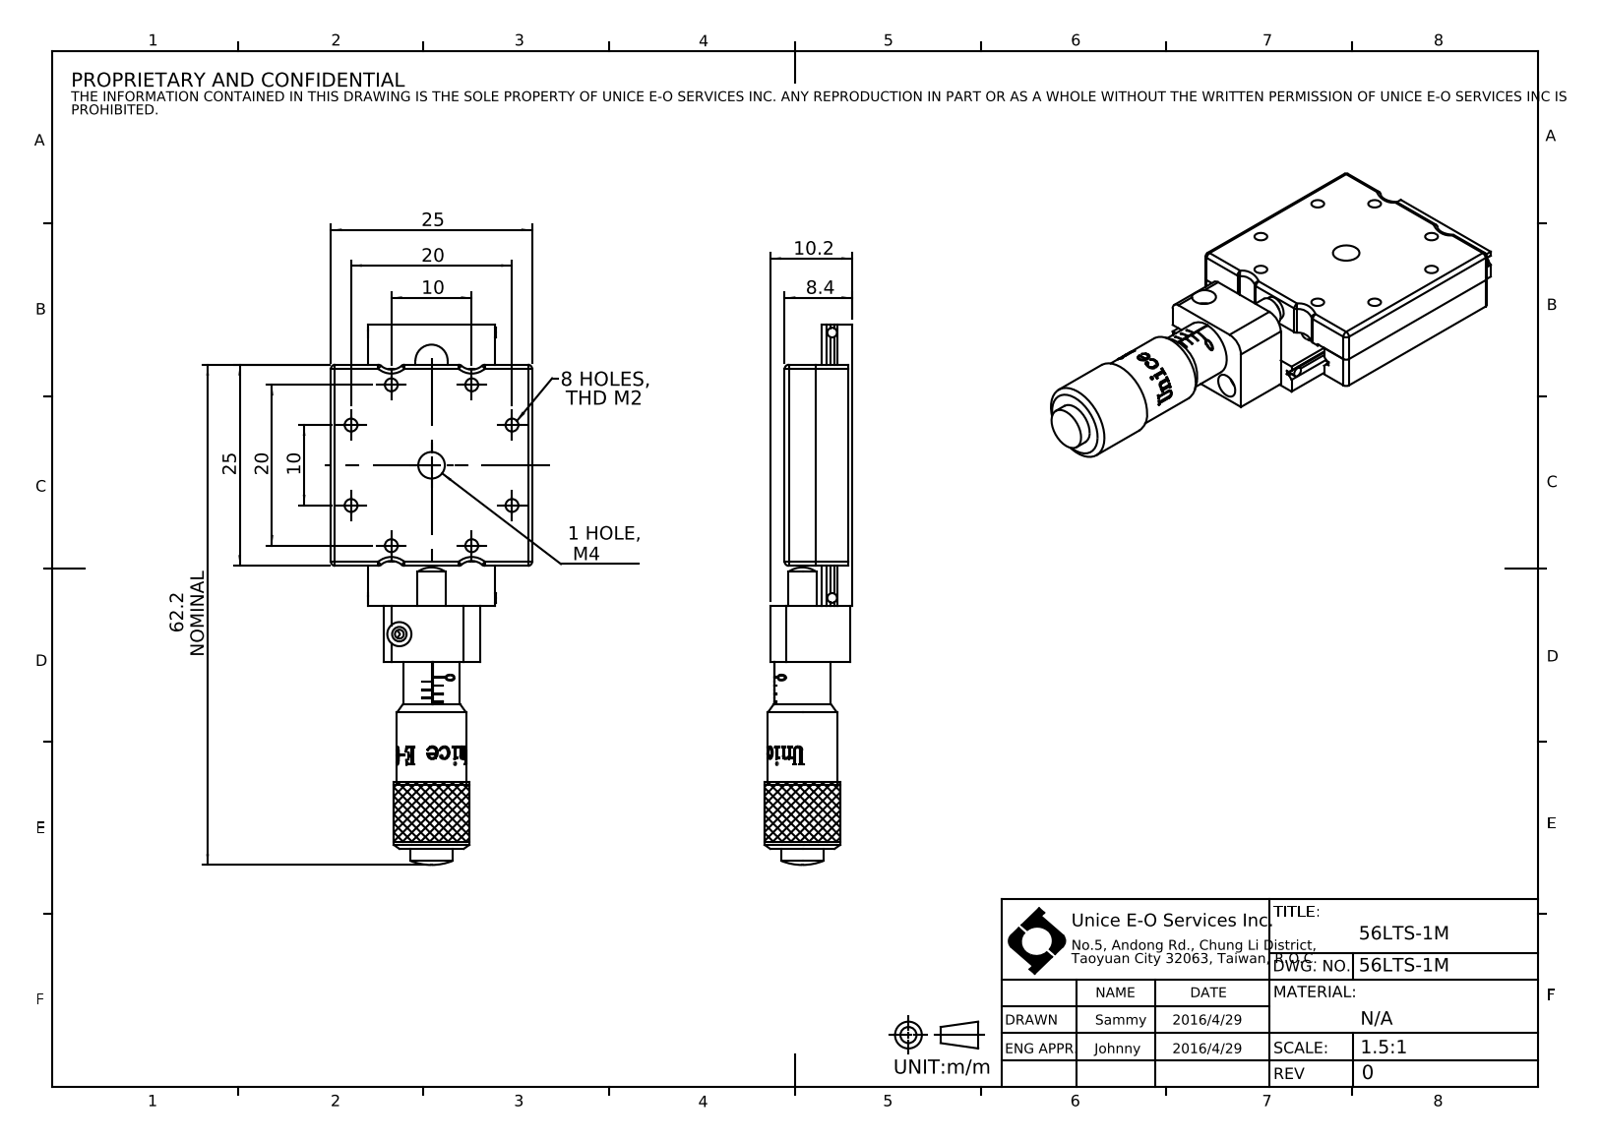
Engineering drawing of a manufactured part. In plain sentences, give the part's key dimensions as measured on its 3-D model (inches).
The part is named "56LTS-1M". Its 3-D file was written by "SolidWorks 2016 (CONFIG_CONTROL_DESIGN)". It is 21 solids with 832 faces: 333 planar, 311 cylindrical and 188 other. Overall it measures 2.646 by 0.984 by 0.429 inches. Its volume is 0.409 cubic inches and its surface area 12.48 square inches. Round holes: 10 of diameter 0.043, 9 of diameter 0.071, 8 of diameter 0.063, 6 of diameter 0.122, 4 of diameter 0.047, 4 of diameter 0.094, 4 of diameter 0.118, 4 of diameter 0.157, 1 of diameter 0.067, 1 of diameter 0.098, 1 of diameter 0.102, 1 of diameter 0.13. Round bosses or shafts: 14 of diameter 0.059, 1 of diameter 0.37, 1 of diameter 0.339, 1 of diameter 0.276, 1 of diameter 0.252, 1 of diameter 0.224, 1 of diameter 0.205, 1 of diameter 0.047. Partial cylindrical surfaces (rounded edges, fillets, slot ends): 16 of radius 0.02, 7 of radius 0.079, 1 of radius 0.039, 1 of radius 0.169. The main face-to-face distances are 0.181, 0.15, 0.028, 0.154, 0.02, 0.331, 0.169, 0.161, 0.177, 0.157. The hole center spacings are 0.44, 0.622, 0.159, 0.198, 0.222, 0.278, 0.354, 0.394.
